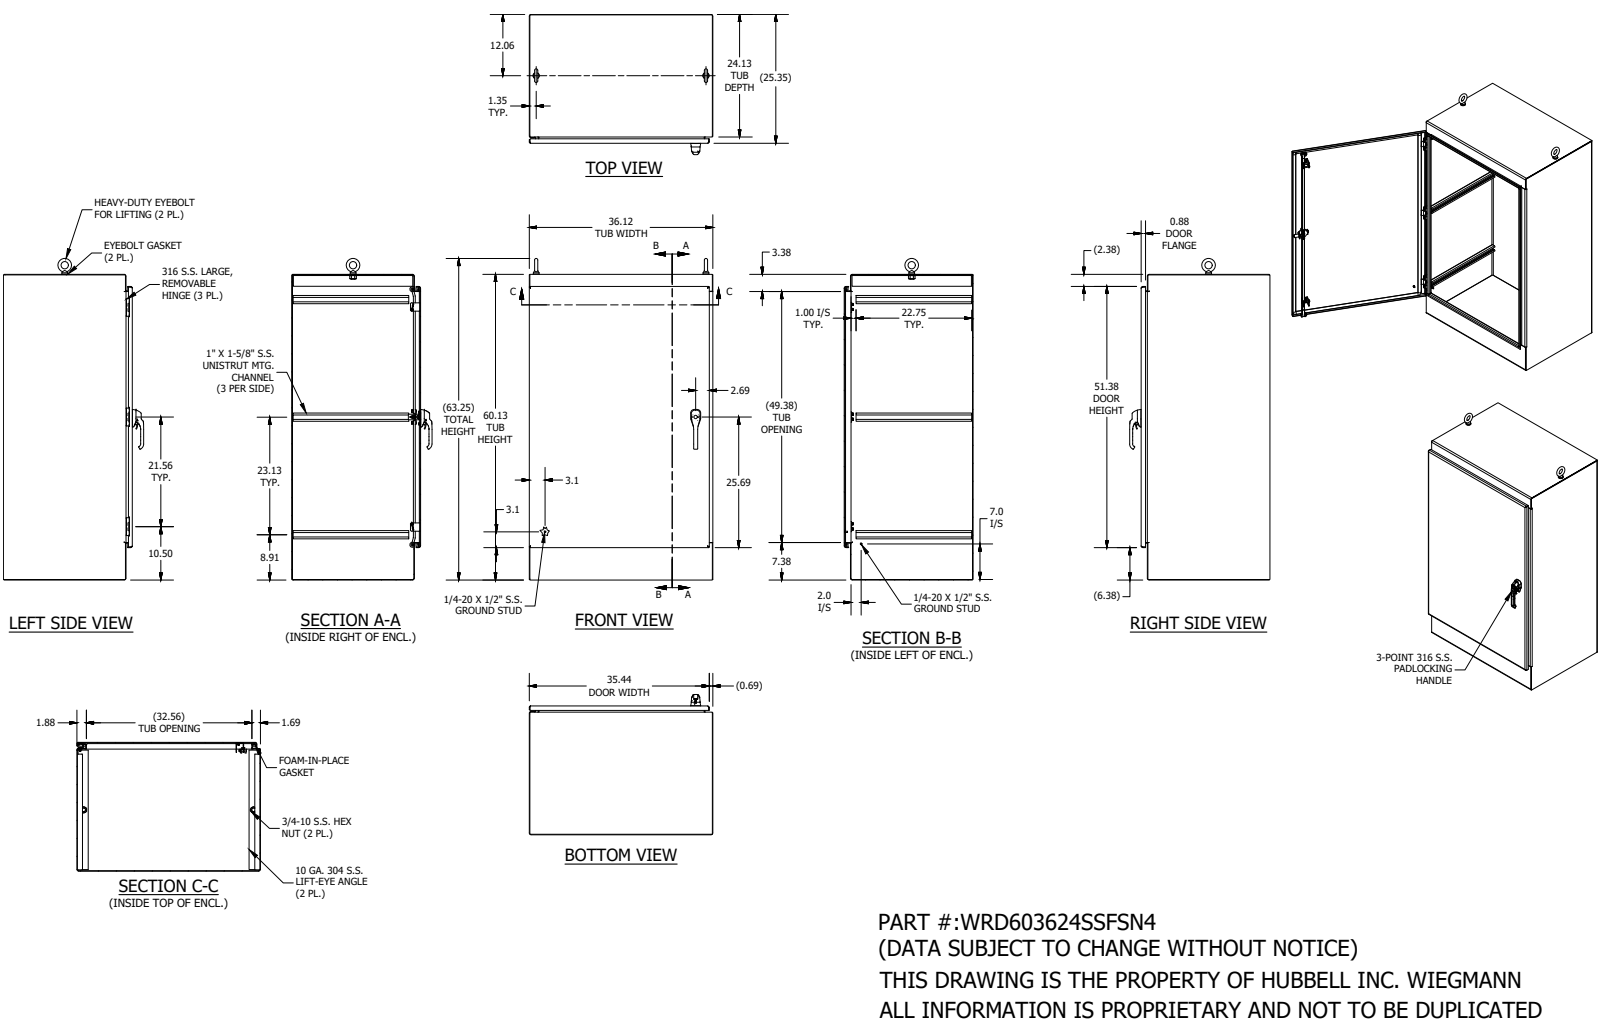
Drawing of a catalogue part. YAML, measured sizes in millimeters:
part_name: "WRD603624SSFSN4"
step_written_by: "SolidWorks 2019 (AUTOMOTIVE_DESIGN)"
units: millimeters
bodies: {solids: 96, faces: 3750, planar: 1523, cylindrical: 1312, other: 915}
overall_size: [1606.5, 917.7, 701]
volume: 18710000
surface_area: 13760000
round_holes:
  - {diameter: 3.6, count: 24}
  - {diameter: 6.7, count: 8}
  - {diameter: 5, count: 6}
  - {diameter: 6.8, count: 6}
  - {diameter: 7.5, count: 6}
  - {diameter: 16.5, count: 6}
  - {diameter: 3.5, count: 4}
  - {diameter: 4.2, count: 4}
  - {diameter: 4.7, count: 4}
  - {diameter: 5.1, count: 4}
  - {diameter: 5.4, count: 3}
  - {diameter: 7.1, count: 3}
round_bosses_or_shafts:
  - {diameter: 15.9, count: 6}
  - {diameter: 6.4, count: 6}
  - {diameter: 6, count: 4}
  - {diameter: 6, count: 3}
  - {diameter: 31.8, count: 2}
  - {diameter: 28.4, count: 2}
  - {diameter: 25.4, count: 2}
  - {diameter: 19.1, count: 2}
partial_cylinders:
  - {radius: 0.5, count: 172}
  - {radius: 0.3, count: 114}
  - {radius: 3.2, count: 32}
  - {radius: 0.5, count: 21}
  - {radius: 1.3, count: 14}
  - {radius: 1.6, count: 14}
  - {radius: 2, count: 14}
  - {radius: 6.4, count: 13}
face_to_face_distances: [2.6, 914.9, 641.2, 638.6, 643.9, 641.2, 2.6, 1524.5, 912.3, 917.6]
hole_center_spacings: [0.5, 0.6, 0.6, 0.7, 9.7, 19.3, 547.7, 25.4]
